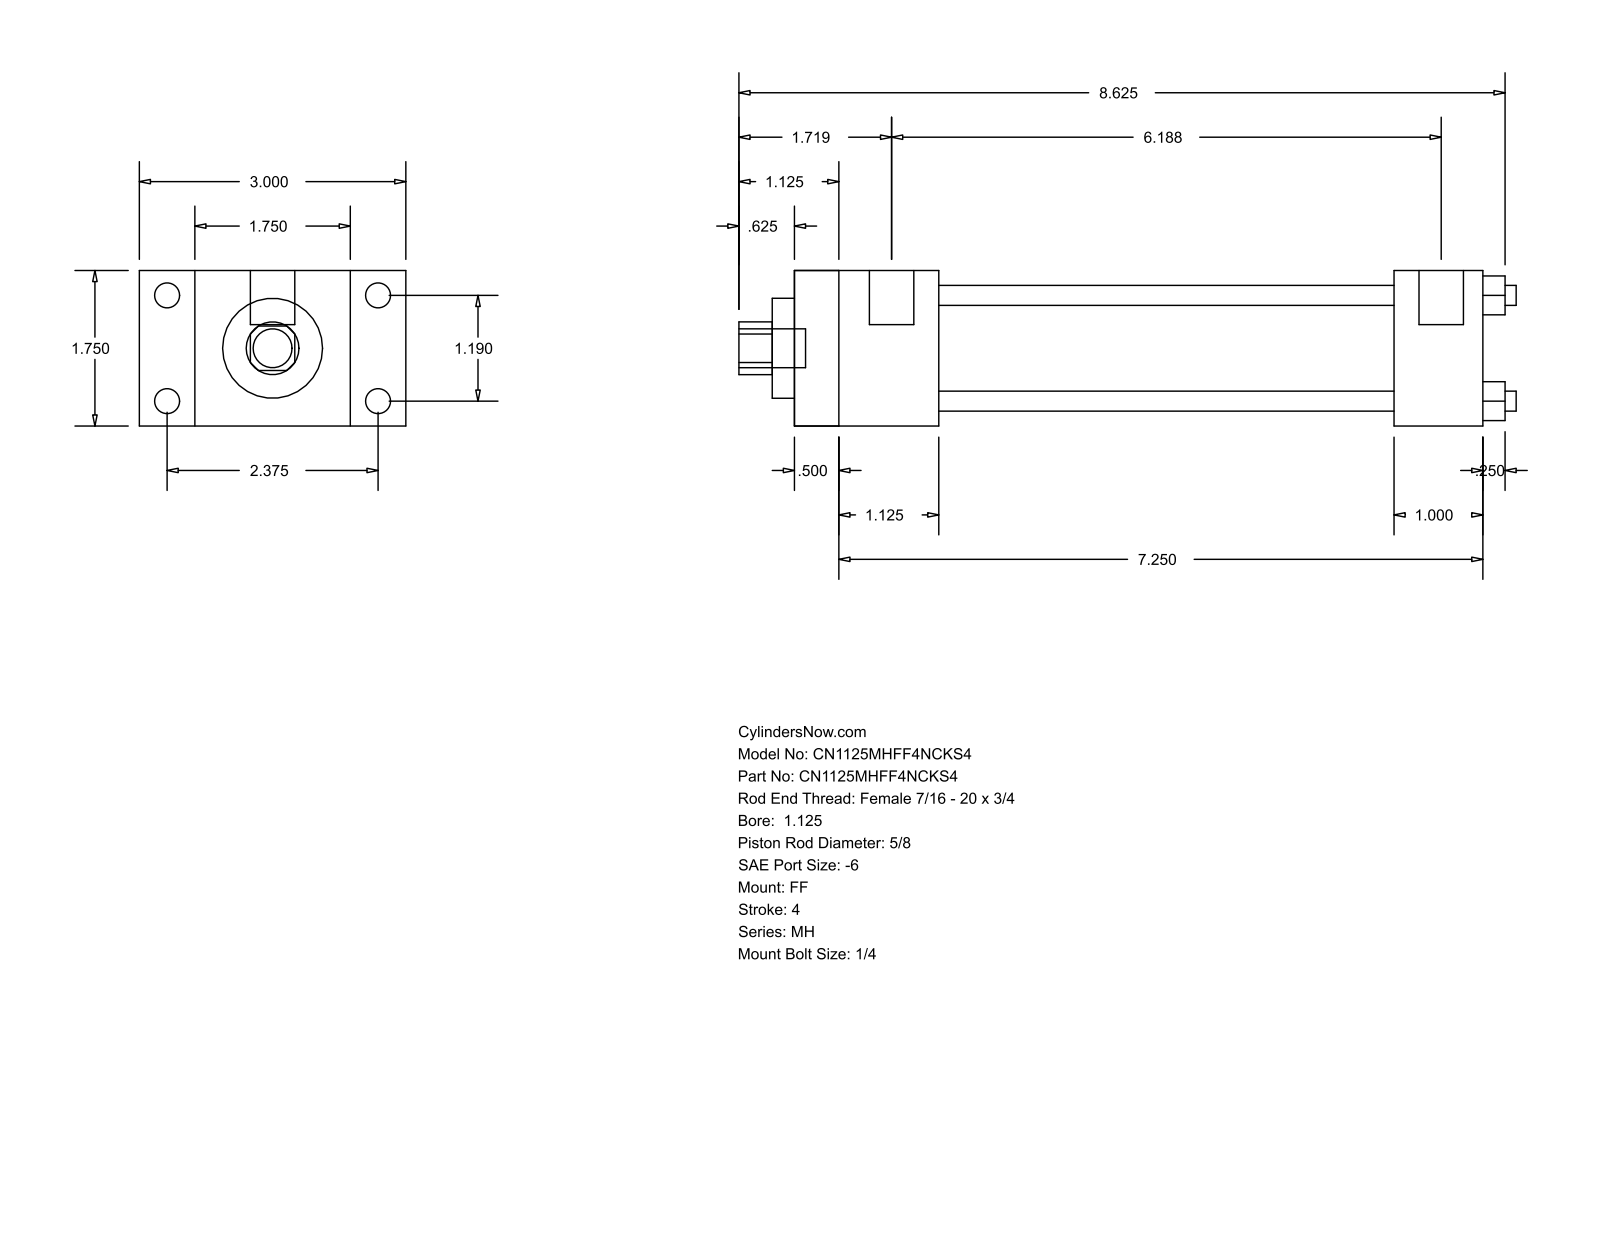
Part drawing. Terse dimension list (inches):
name: MH_FF__0112_0.625
written by: GSSL Pune (CONFIG_CONTROL_DESIGN)
unit: in
bodies: 0 solids, 92 faces (64 planar, 28 cylindrical, 0 other)
size: 8.75 × 3 × 1.75
holes: 4× ⌀0.225, 1× ⌀0.625, 1× ⌀1.125, 1× ⌀1.375
bosses: 4× ⌀0.281, 4× ⌀0.219, 2× ⌀0.5, 1× ⌀0.437
rounds: 1× R0.297
face distances: 1.75, 7.75, 0.625, 0.5, 7.25, 2.375, 1.125, 1.625, 6.75, 6.25
hole spacings: 0.841, 1.19, 1.683
